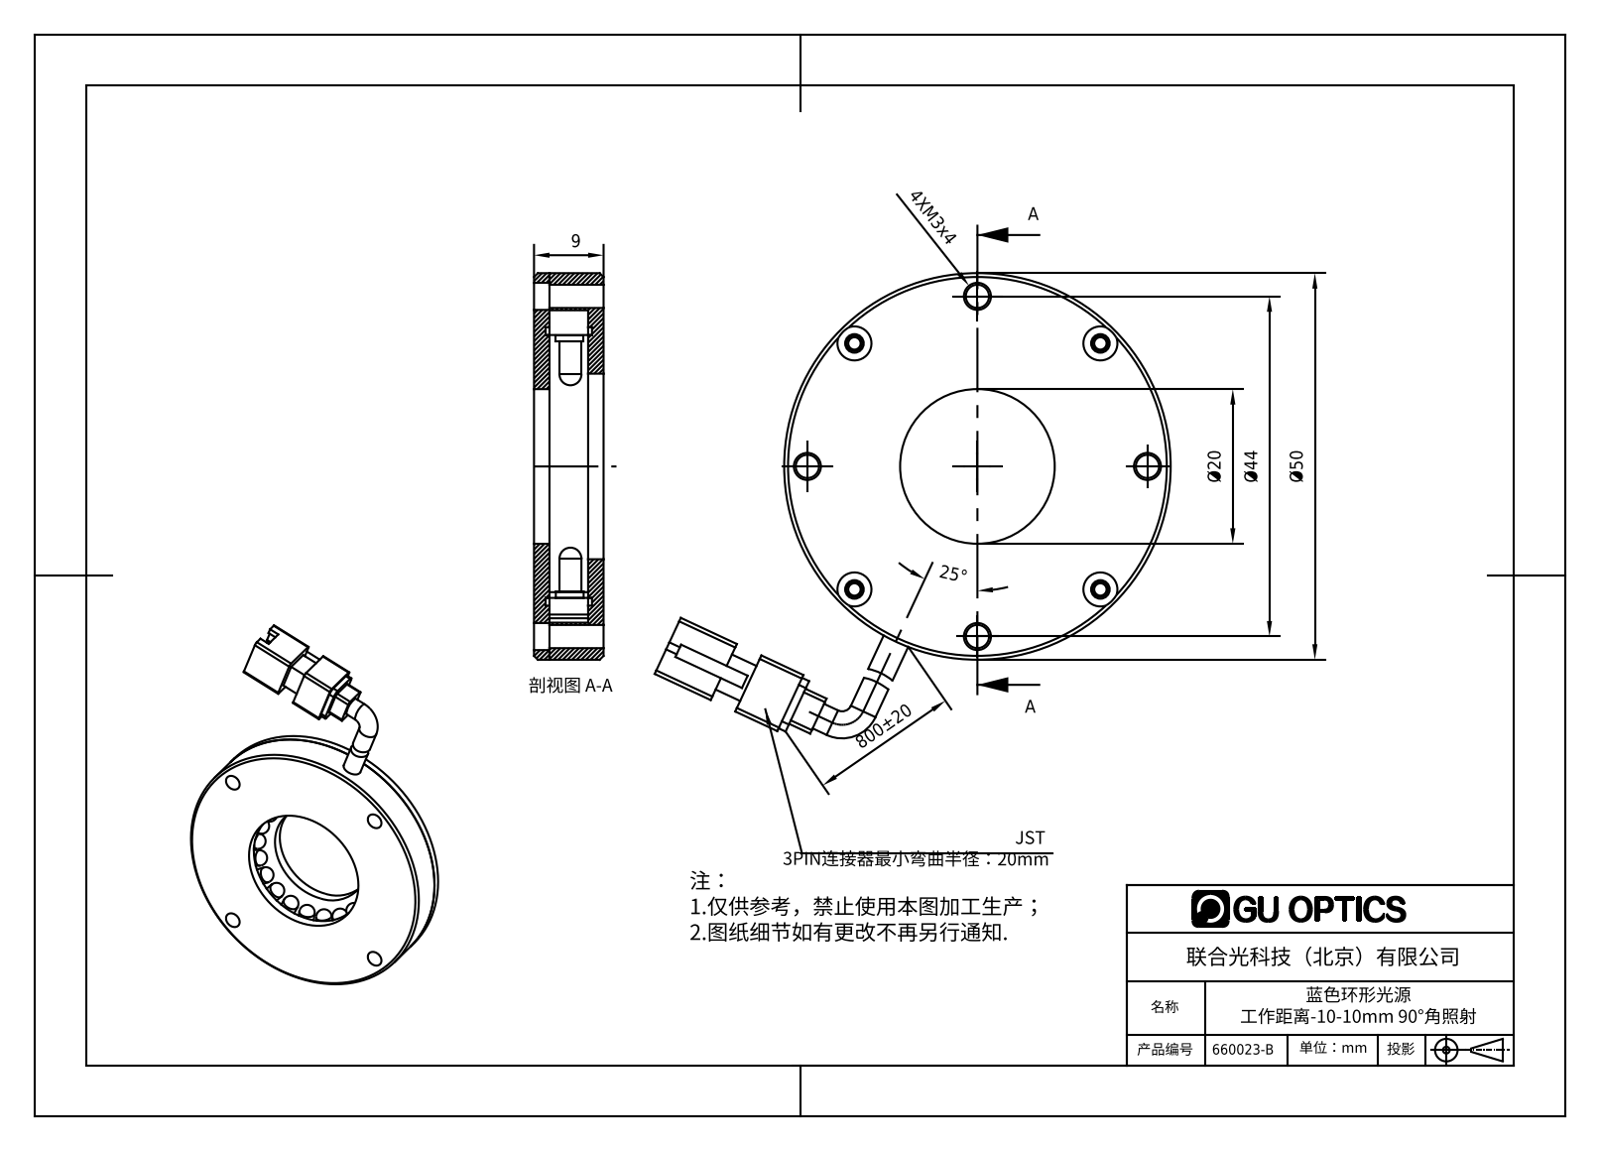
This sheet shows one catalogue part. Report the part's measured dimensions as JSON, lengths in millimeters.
{"part_name": "660023-B", "step_written_by": "SolidWorks 2016 (AUTOMOTIVE_DESIGN)", "units": "millimeters", "bodies": {"solids": 26, "faces": 561, "planar": 329, "cylindrical": 187, "other": 45}, "overall_size": [73.5, 50, 10], "volume_mm3": 11250, "surface_area_mm2": 13403, "round_holes": [[3, 5], [3.5, 5], [1.6, 4], [2, 4], [2.4, 4], [20, 1], [24, 1], [36, 1], [40.4, 1]], "round_bosses_or_shafts": [[3.8, 21], [3, 21], [3.5, 2], [50, 1], [34.4, 1], [34, 1]], "partial_cylinders_radius": [[0.5, 12], [1, 4]], "face_to_face_distances": [7, 2, 9, 5, 0.5, 1, 5.5, 1.5, 6, 7.5], "hole_center_spacings": [17.04, 22.5, 31.82, 41.11, 41.12, 17.03, 22, 22.01]}
